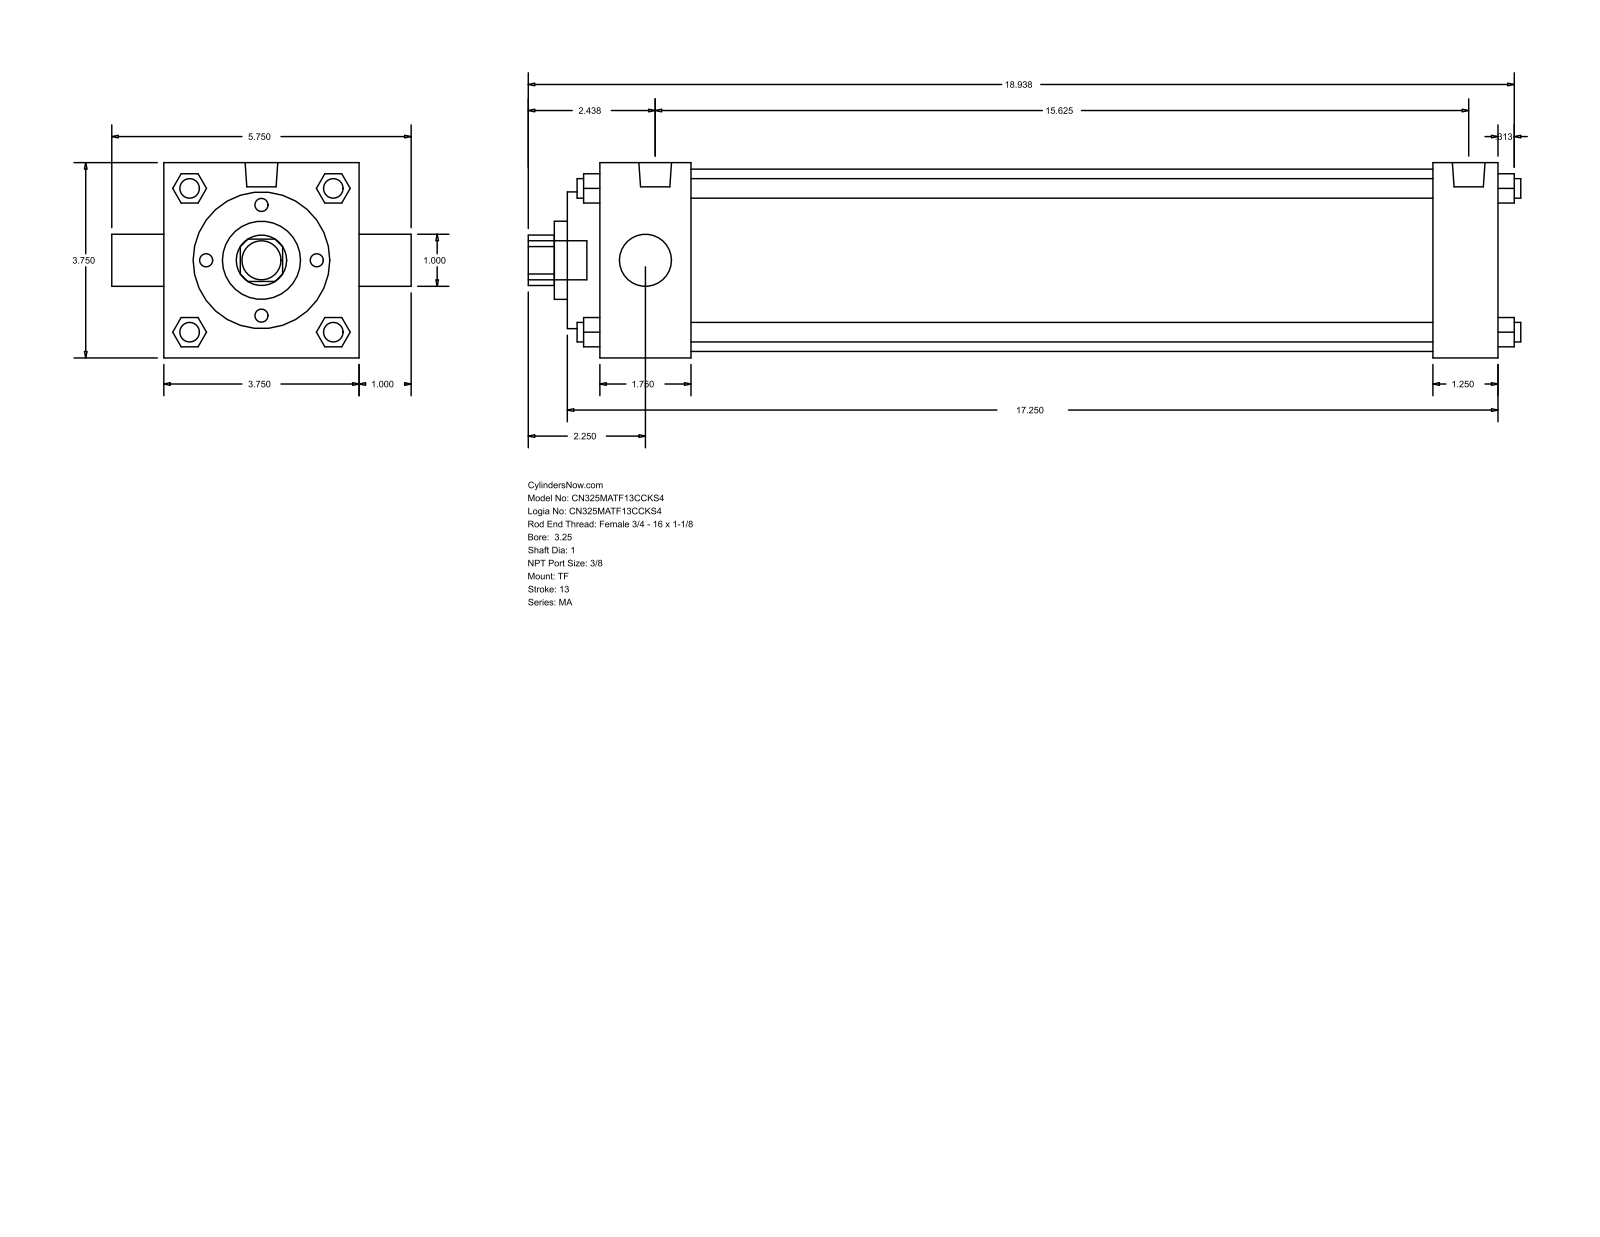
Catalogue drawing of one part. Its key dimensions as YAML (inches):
part_name: "MA_TF__0325_1"
step_written_by: "GSSL Pune (CONFIG_CONTROL_DESIGN)"
units: inches
bodies: {solids: 0, faces: 122, planar: 93, cylindrical: 29, other: 0}
overall_size: [19.063, 5.75, 3.75]
round_holes:
  - {diameter: 1, count: 2}
  - {diameter: 1.5, count: 1}
  - {diameter: 2.625, count: 1}
  - {diameter: 3.5, count: 1}
round_bosses_or_shafts:
  - {diameter: 0.375, count: 4}
  - {diameter: 0.437, count: 3}
  - {diameter: 0.627, count: 2}
  - {diameter: 0.75, count: 1}
partial_cylinders:
  - {radius: 0.484, count: 1}
face_to_face_distances: [3.75, 17.25, 17.875, 0.625, 1.75, 16, 14.25, 15.5, 1.25, 2.375]
